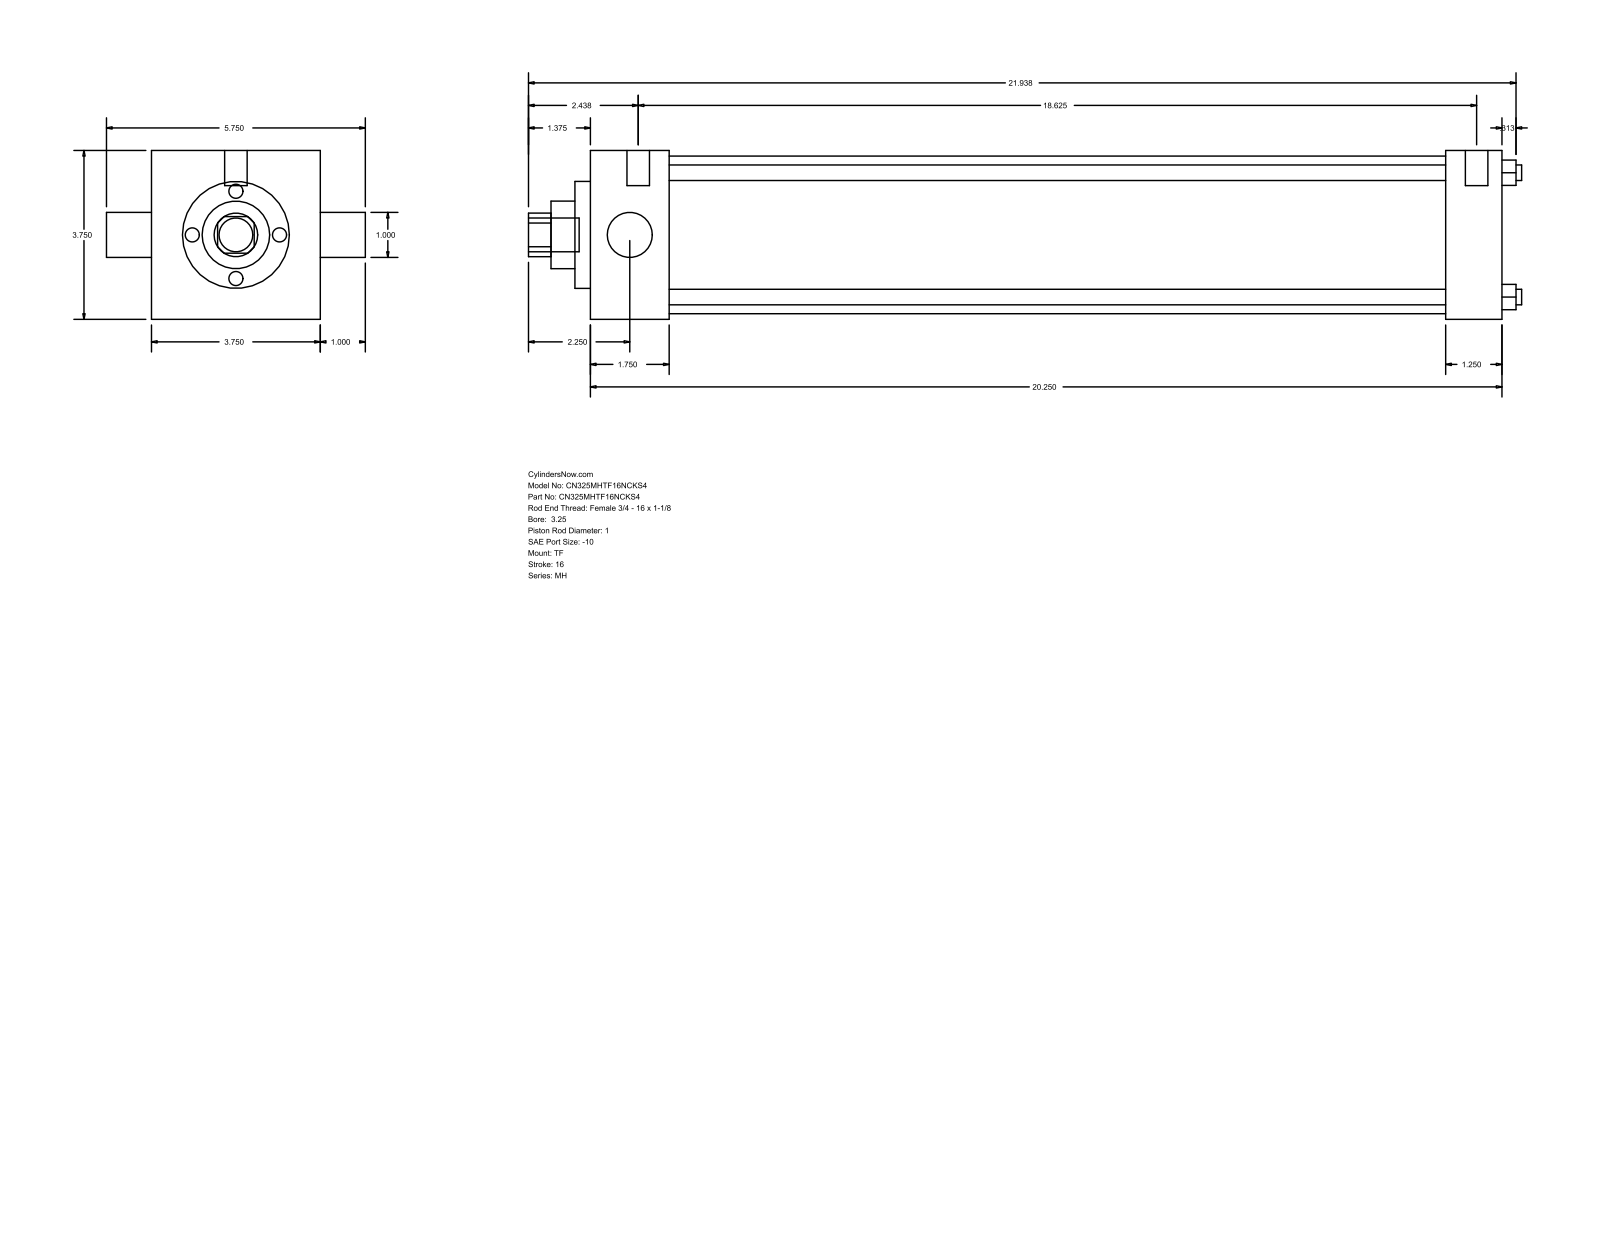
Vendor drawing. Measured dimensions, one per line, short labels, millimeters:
name: MH_TF__0325_1
written by: GSSL Pune (CONFIG_CONTROL_DESIGN)
unit: mm
bodies: 0 solids, 86 faces (61 planar, 25 cylindrical, 0 other)
size: 560.39 × 146.05 × 95.25
holes: 4× ⌀8.76, 2× ⌀25.4, 1× ⌀38.1, 1× ⌀60.33, 1× ⌀88.9
bosses: 3× ⌀5.56, 2× ⌀12.7, 1× ⌀19.05
rounds: 1× R12.29
face distances: 95.24, 514.35, 44.46, 482.6, 438.14, 469.89, 31.75, 8.73, 53.19, 491.33
hole spacings: 49.57, 70.1, 99.14
